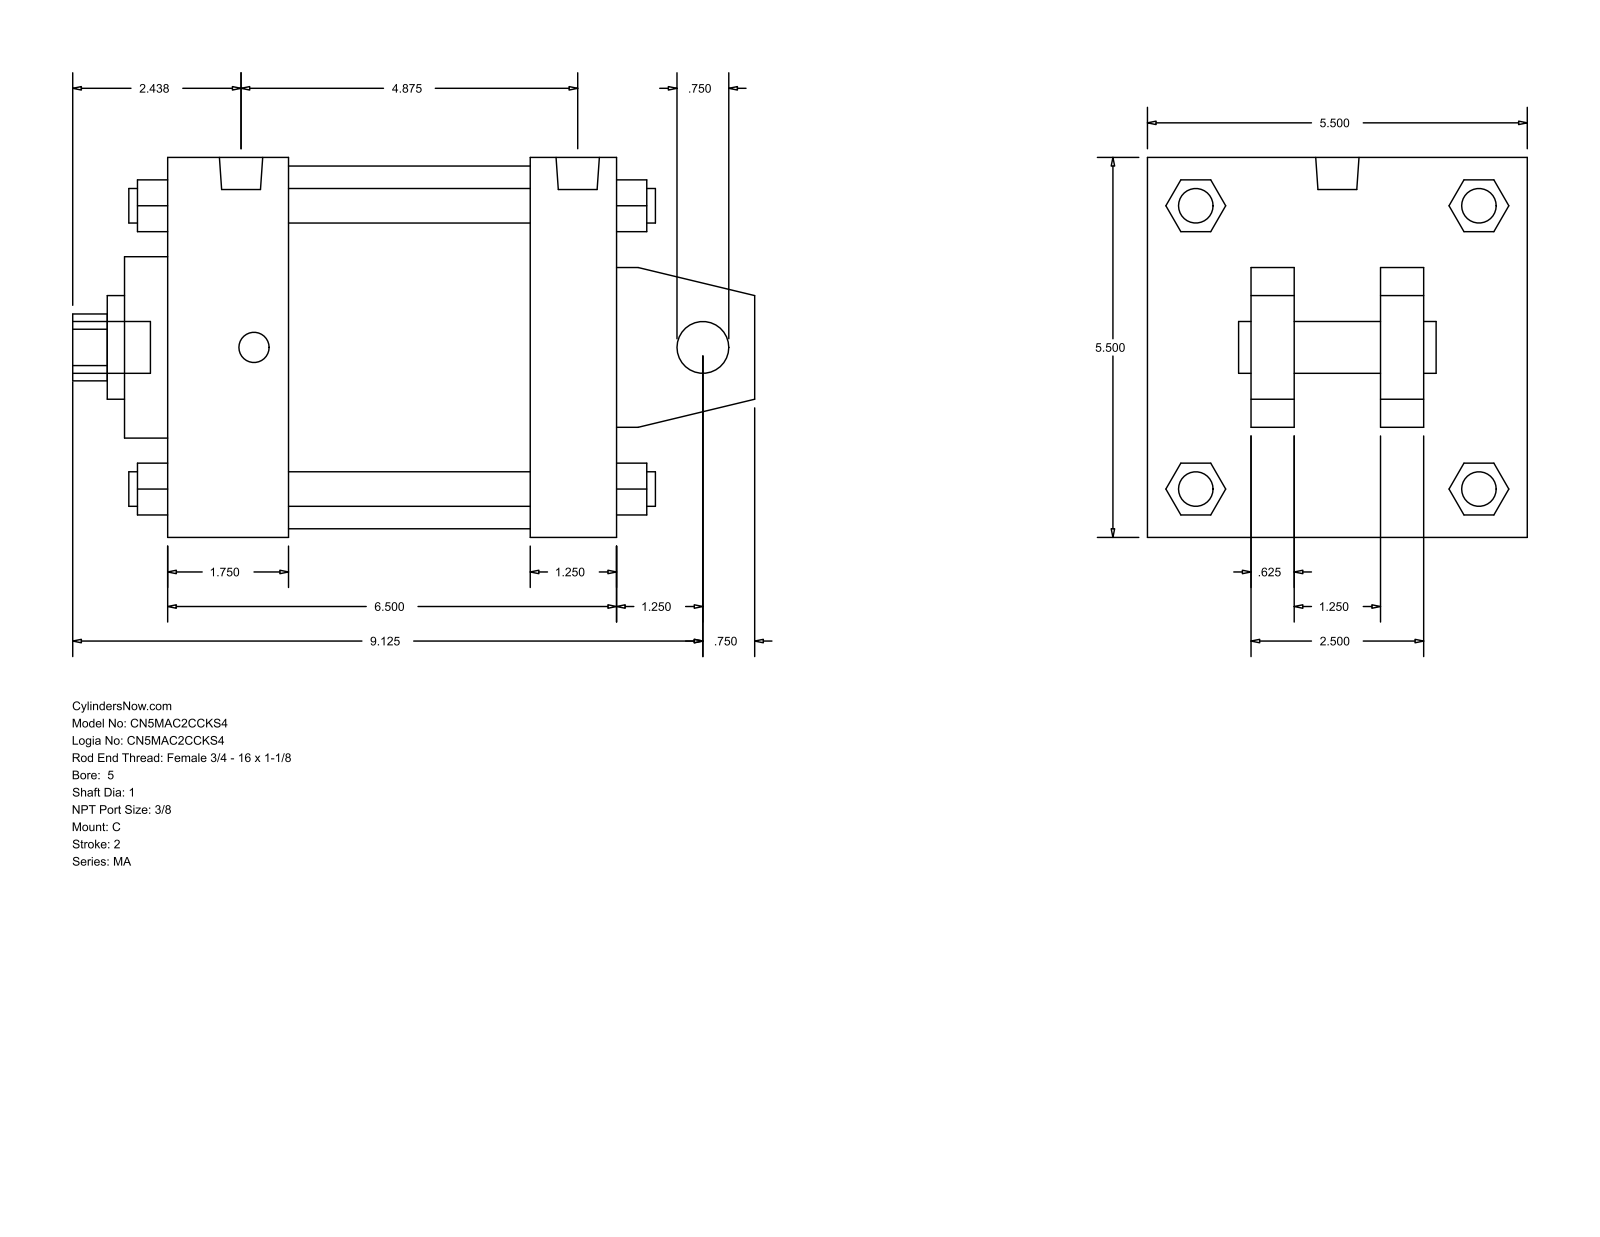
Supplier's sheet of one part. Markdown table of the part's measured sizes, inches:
| quantity | value |
| --- | --- |
| part name | MA_C__0500_1 |
| STEP written by | GSSL Pune (CONFIG_CONTROL_DESIGN) |
| units | inches |
| bodies | 0 solids, 141 faces (109 planar, 32 cylindrical, 0 other) |
| overall size | 9.875 × 5.5 × 5.5 |
| round holes (diameter × count) | 0.75 × 1, 1 × 1, 1.5 × 1, 2.625 × 1, 5.25 × 1 |
| round bosses / shafts (diameter × count) | 0.5 × 4, 0.437 × 4, 0.627 × 2, 0.75 × 1 |
| partial cylindrical surfaces (radius × count) | 0.484 × 1 |
| main face-to-face distances | 5.5, 6.5, 0.625, 5.25, 1.25, 1.75, 3.5, 4.75, 1.5, 4 |
